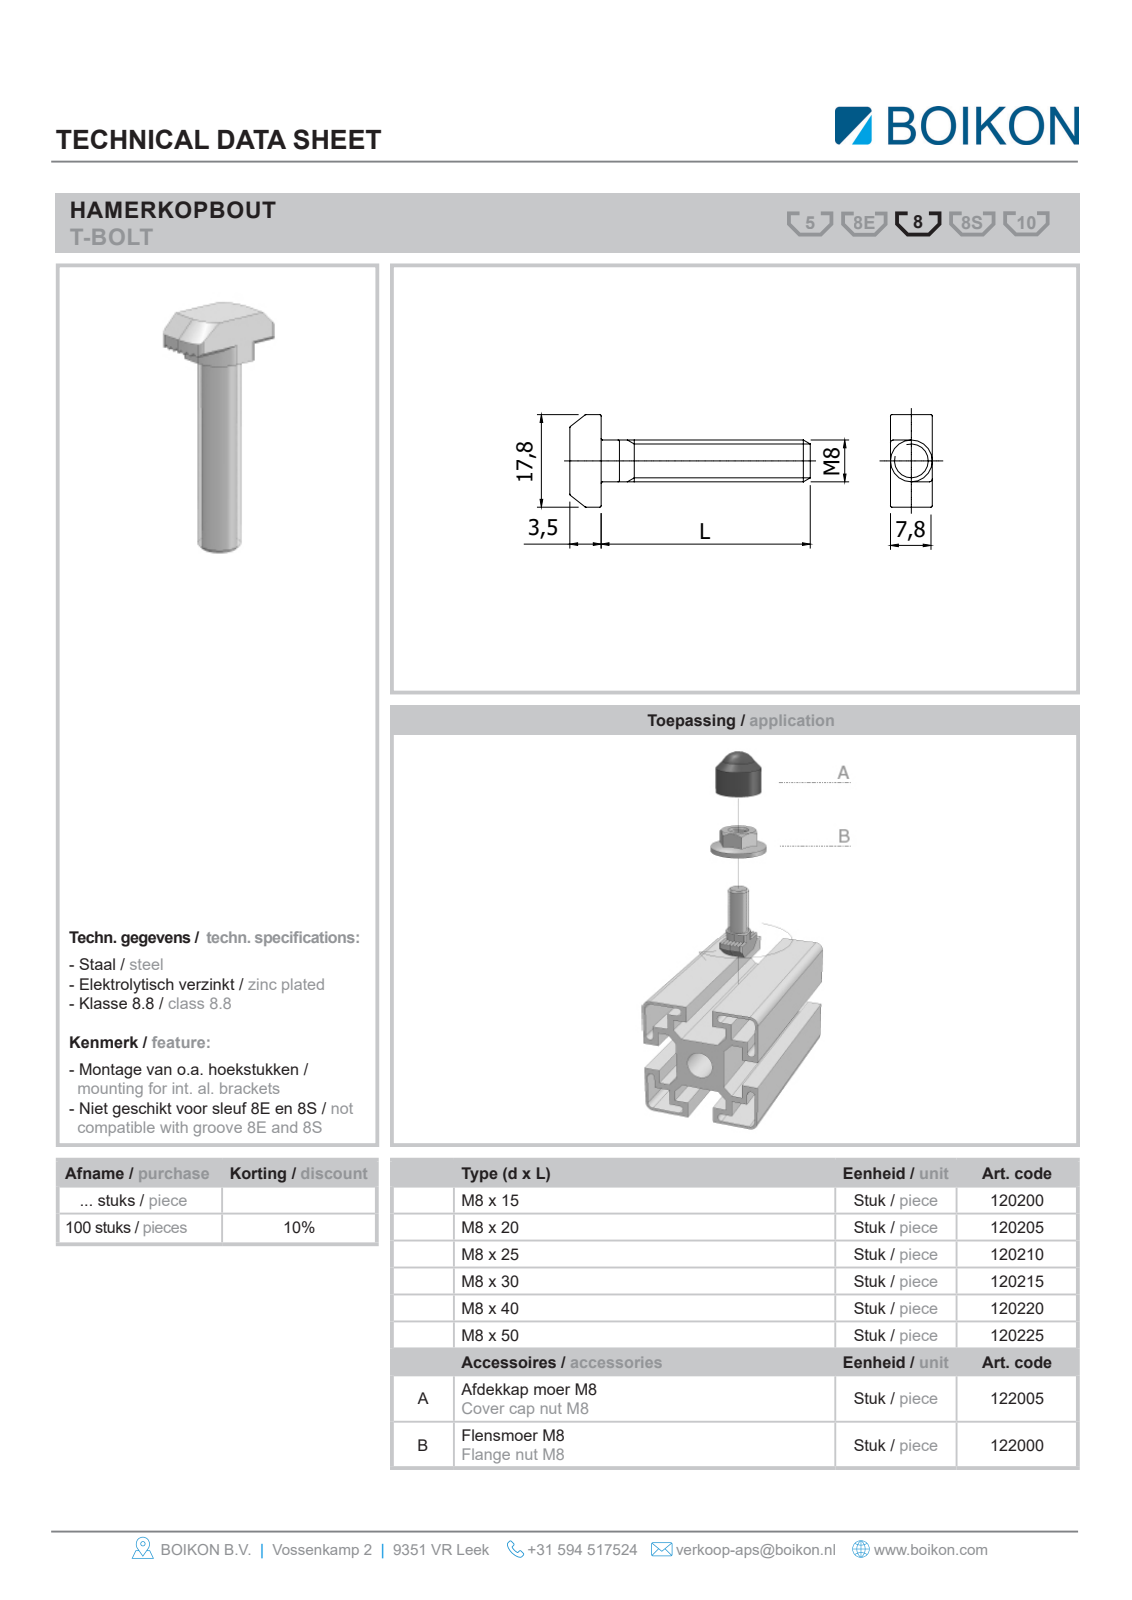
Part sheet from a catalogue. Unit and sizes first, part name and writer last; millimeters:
Units: millimetres
Overall size (bounding box): 30.7 × 19.4 × 8.5
Round bosses / shafts (diameter × count): ⌀6.47 ×1
Partial cylindrical surfaces — rounded edges, fillets, slot ends (radius × count): R1 ×4, R0.4 ×2, R5 ×1, R9.7 ×1
Main face-to-face distances: 8.5, 0.71, 2.12, 1.41, 2.83, 8.7, 1.42, 30.7, 22, 4.24
Volume: 1 723 mm³ · Surface area: 1 132 mm²
Bodies: 1 solid, 60 faces (47 planar, 11 cylindrical, 2 other)
Part name (STEP PRODUCT): Root; 120210 - Hamerkopbout M8 x 25 BOIKON
STEP written by: HiCAD 2013 1802.4 Build 509 (AUTOMOTIVE_DESIGN)
